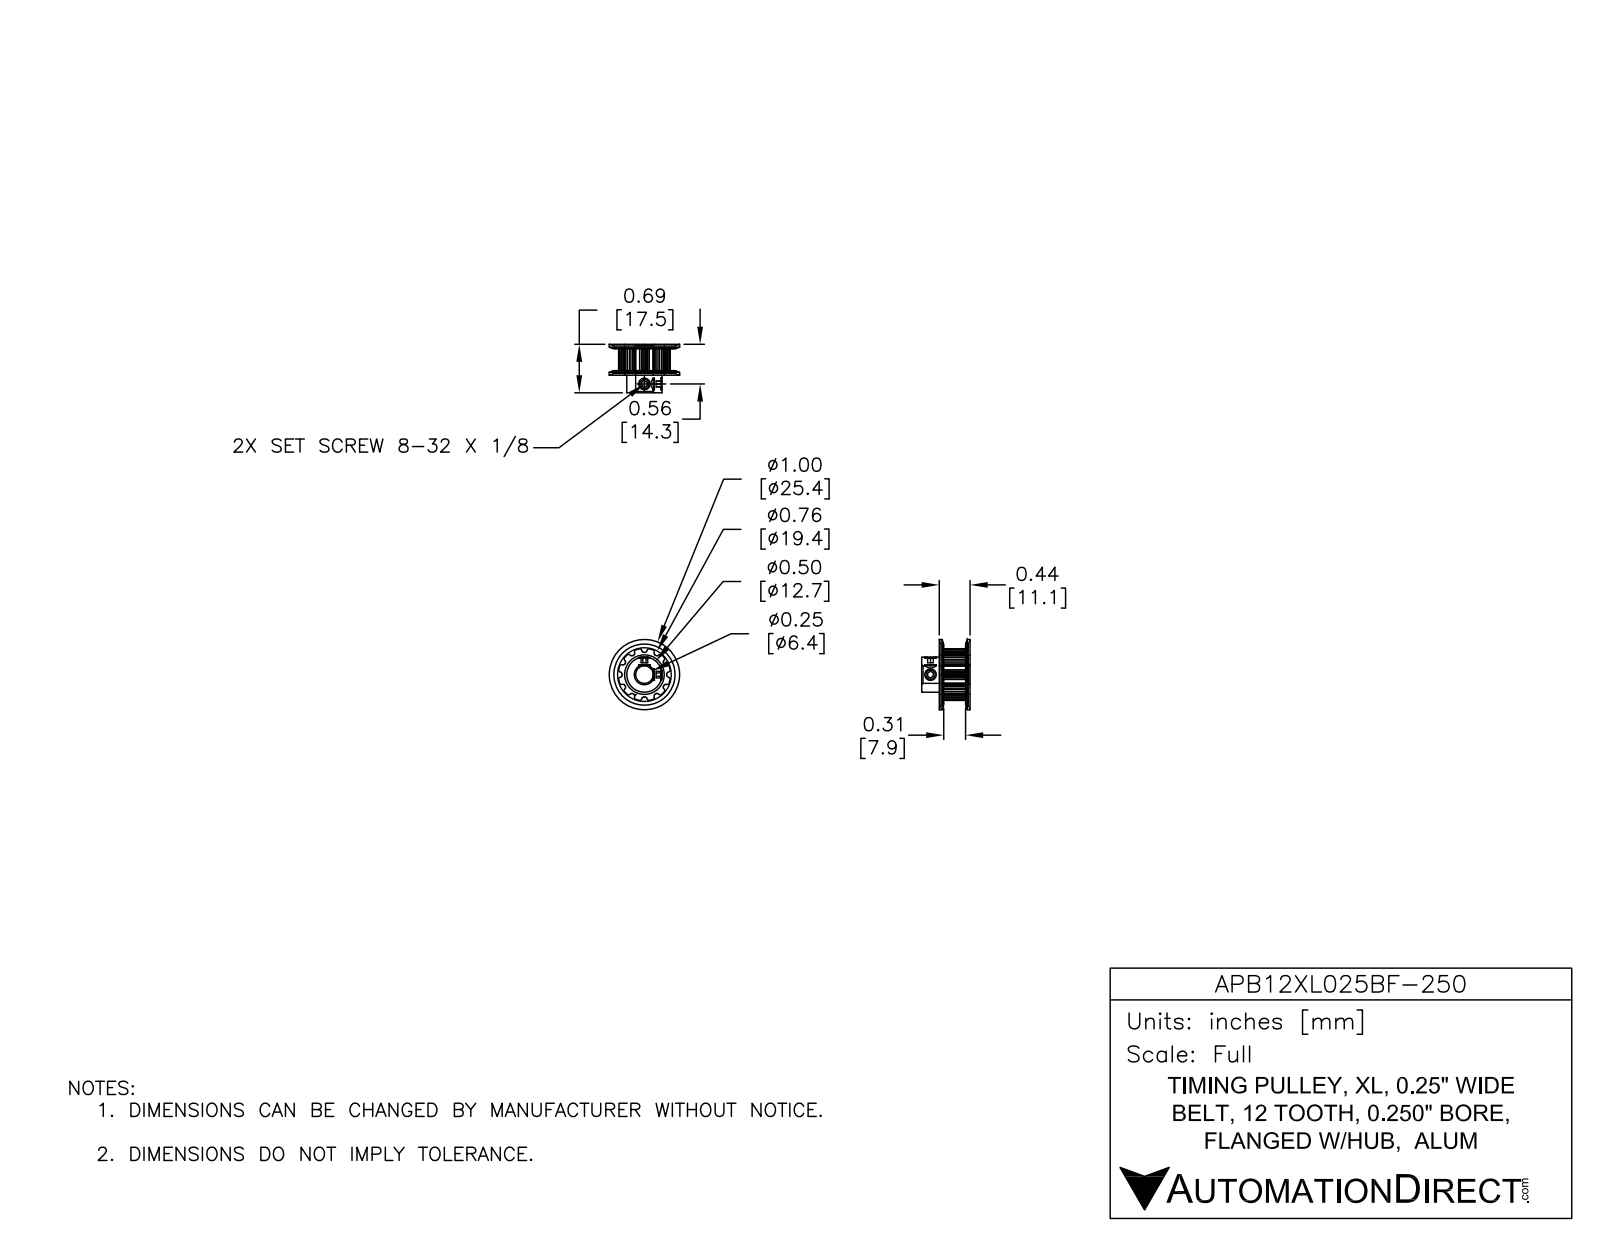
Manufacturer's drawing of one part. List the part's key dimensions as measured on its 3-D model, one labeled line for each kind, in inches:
Part name (STEP PRODUCT): APB12XL025BF-250
STEP written by: SolidWorks 2014 (AUTOMOTIVE_DESIGN)
Units: inches
Bodies: 1 solid, 141 faces (42 planar, 77 cylindrical, 22 other)
Overall size (bounding box): 1 × 1 × 0.688
Volume: 0.196 in³ · Surface area: 4.452 in²
Round holes (diameter × count): ⌀0.088 ×2, ⌀0.25 ×1
Round bosses / shafts (diameter × count): ⌀0.5 ×1
Partial cylindrical surfaces — rounded edges, fillets, slot ends (radius × count): R0.015 ×48, R0.317 ×1
Main face-to-face distances: 0.375, 0.032, 0.343, 0.033, 0.407, 0.744, 0.688, 0.656, 0.281, 0.221
